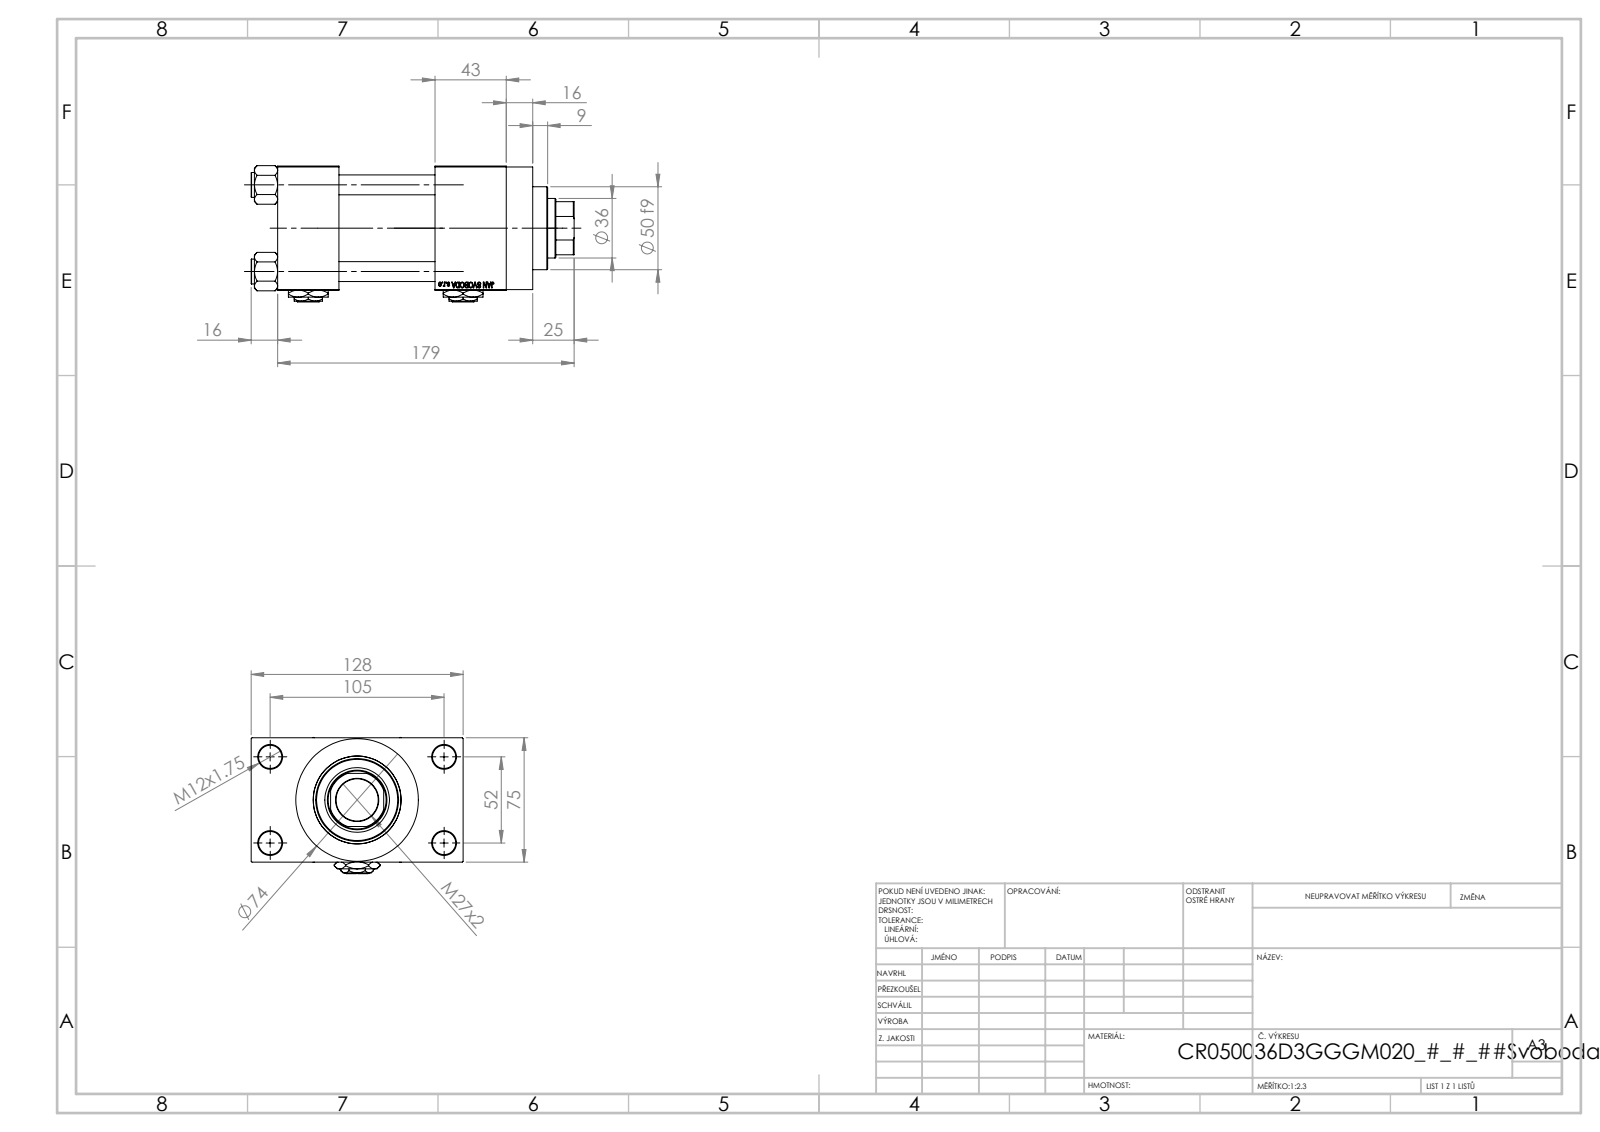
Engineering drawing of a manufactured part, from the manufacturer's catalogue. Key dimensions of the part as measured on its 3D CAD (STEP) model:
Part name (STEP PRODUCT): Zatka_pro_OIL_PORT; V215CR_D_Body; NUT_M5_D; V215CR_D_TYCINKA (+2 more)
STEP written by: SolidWorks 2019 (CONFIG_CONTROL_DESIGN)
Units: millimetres
Bodies: 13 solids, 1205 faces (545 planar, 100 cylindrical, 560 other)
Overall size (bounding box): 195 × 128 × 82.27
Volume: 821 972 mm³ · Surface area: 178 028 mm²
Round holes (diameter × count): ⌀12 ×4, ⌀14 ×4, ⌀7 ×2, ⌀20.96 ×2, ⌀30 ×2, ⌀25.5 ×1, ⌀36 ×1, ⌀39 ×1, ⌀41 ×1, ⌀53 ×1
Round bosses / shafts (diameter × count): ⌀15 ×4, ⌀74 ×1, ⌀56 ×1, ⌀50 ×1
Partial cylindrical surfaces — rounded edges, fillets, slot ends (radius × count): R17.5 ×1
Main face-to-face distances: 75, 58, 37, 95, 101.5, 26.5, 138, 43, 101, 16
Hole centre spacings: 26.35, 36.98, 52.3, 58.43, 58.59, 78.65, 94.37, 52
